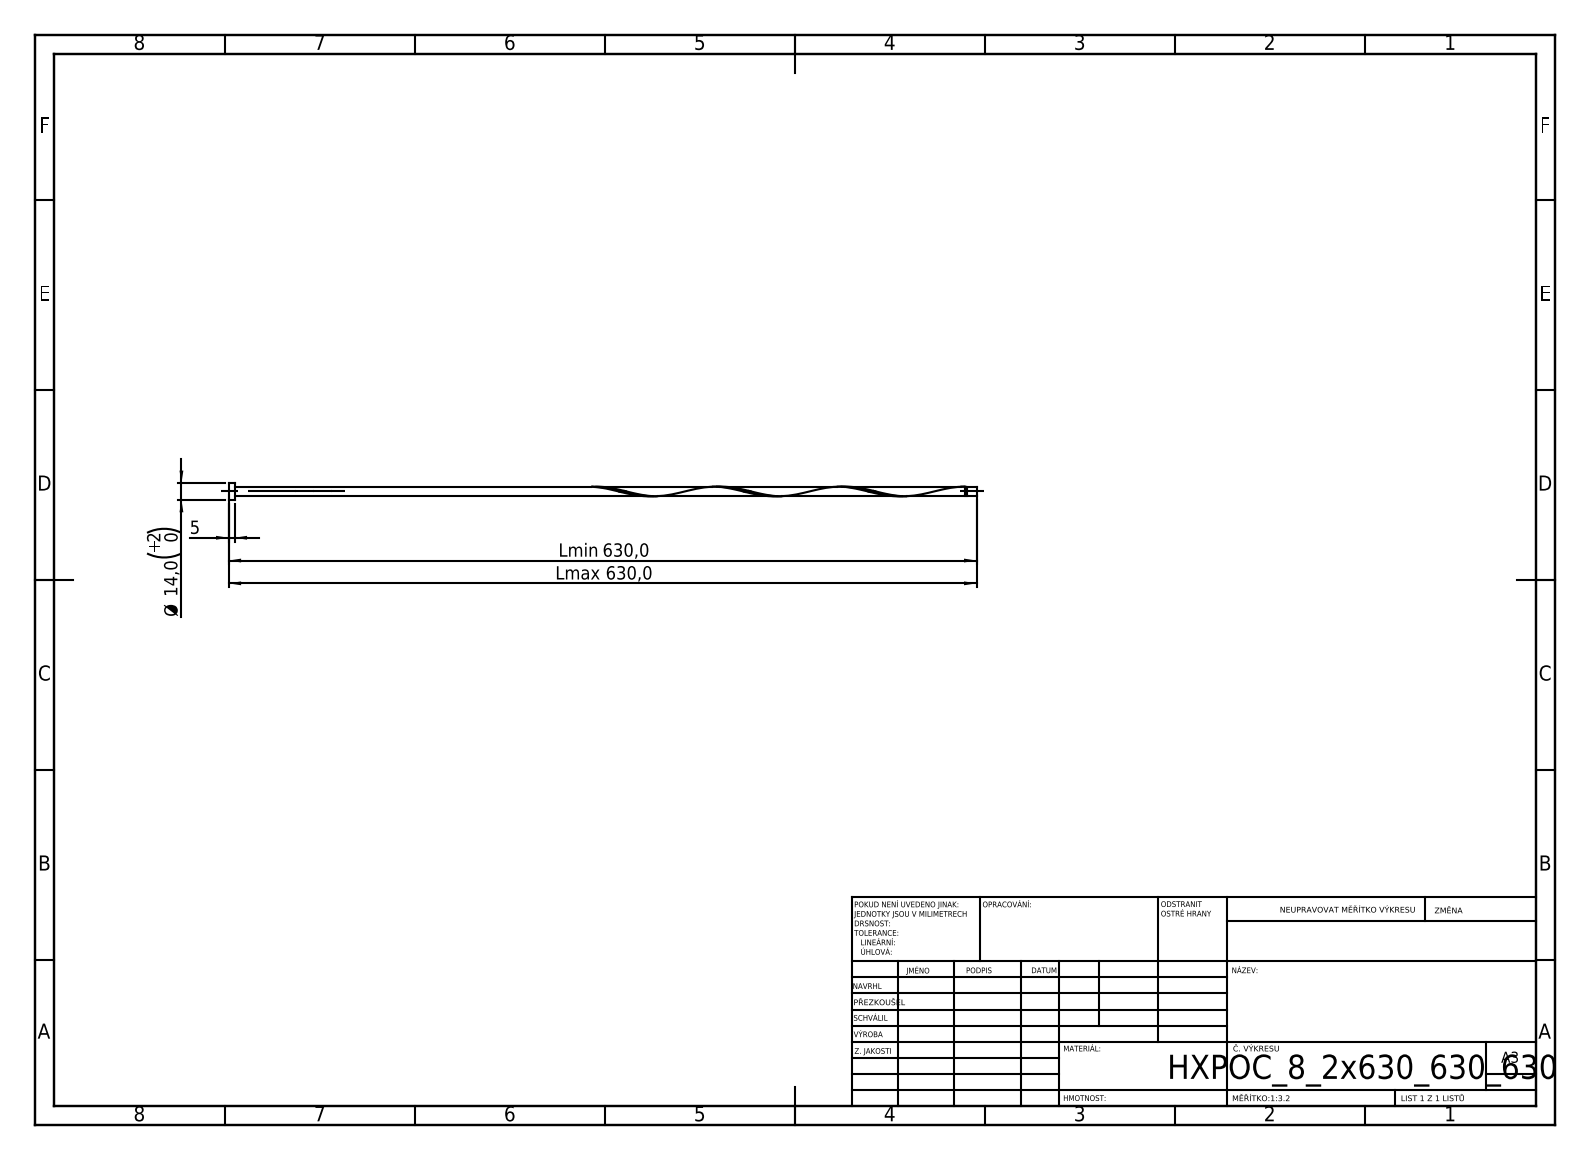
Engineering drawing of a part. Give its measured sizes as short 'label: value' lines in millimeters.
written by: SolidWorks 2019 (CONFIG_CONTROL_DESIGN)
unit: mm
bodies: 1 solid, 16 faces (6 planar, 9 cylindrical, 1 other)
size: 630 × 14 × 14
volume: 40 819 mm³; area: 22 320 mm²
bosses: 1× ⌀14, 1× ⌀8.2, 1× ⌀6.56
face distances: 5, 630, 625, 622.19, 617.19, 7.81, 620.55, 615.55, 1.64, 9.45
